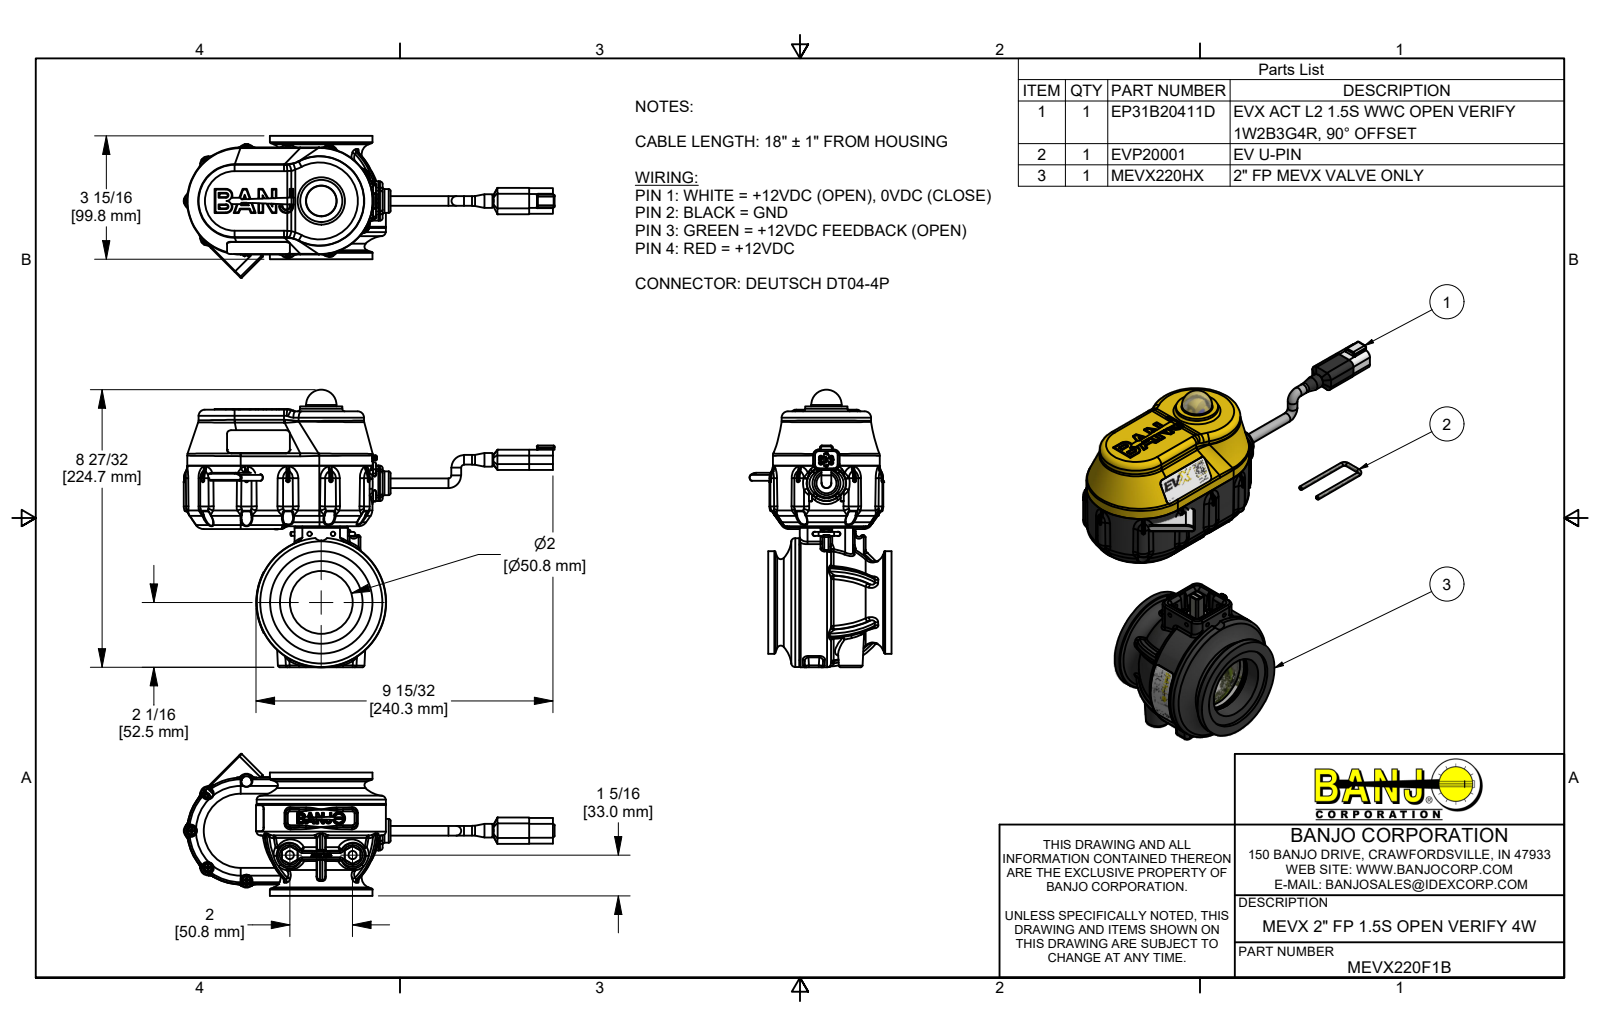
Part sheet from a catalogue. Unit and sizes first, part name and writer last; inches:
Units: inches
Overall size (bounding box): 11.82 × 8.846 × 4.526
Round holes (diameter × count): ⌀0.095 ×11, ⌀0.15 ×11, ⌀0.135 ×6, ⌀0.02 ×4, ⌀0.03 ×4, ⌀0.061 ×4, ⌀0.107 ×4, ⌀0.126 ×4, ⌀0.136 ×4, ⌀0.15 ×4, ⌀0.17 ×4, ⌀0.105 ×2
Round bosses / shafts (diameter × count): ⌀0.08 ×20, ⌀0.25 ×16, ⌀0.14 ×10, ⌀0.108 ×10, ⌀0.085 ×10, ⌀0.058 ×8, ⌀0.27 ×4, ⌀0.219 ×4
Partial cylindrical surfaces — rounded edges, fillets, slot ends (radius × count): R0.013 ×180, R0.04 ×141, R0.02 ×84, R0.01 ×83, R0.005 ×57, R0.015 ×52, R0.03 ×43, R0.125 ×35
Main face-to-face distances: 0.1, 2.565, 2.465, 0.05, 1.685, 0.78, 0.88, 1.142, 1.242, 2.022
Hole centre spacings: 0.75, 0.165, 2.485, 2.73, 3.45, 0.34, 0.378, 0.487
Volume: 52.74 in³ · Surface area: 596.4 in²
Bodies: 80 solids, 10768 faces (2591 planar, 3192 cylindrical, 4985 other)
Part name (STEP PRODUCT): MEVX220F1B; EVP20001; MEVX220HX; AQ206V (+8 more)
STEP written by: Autodesk Inventor 2022 (AUTOMOTIVE_DESIGN)
